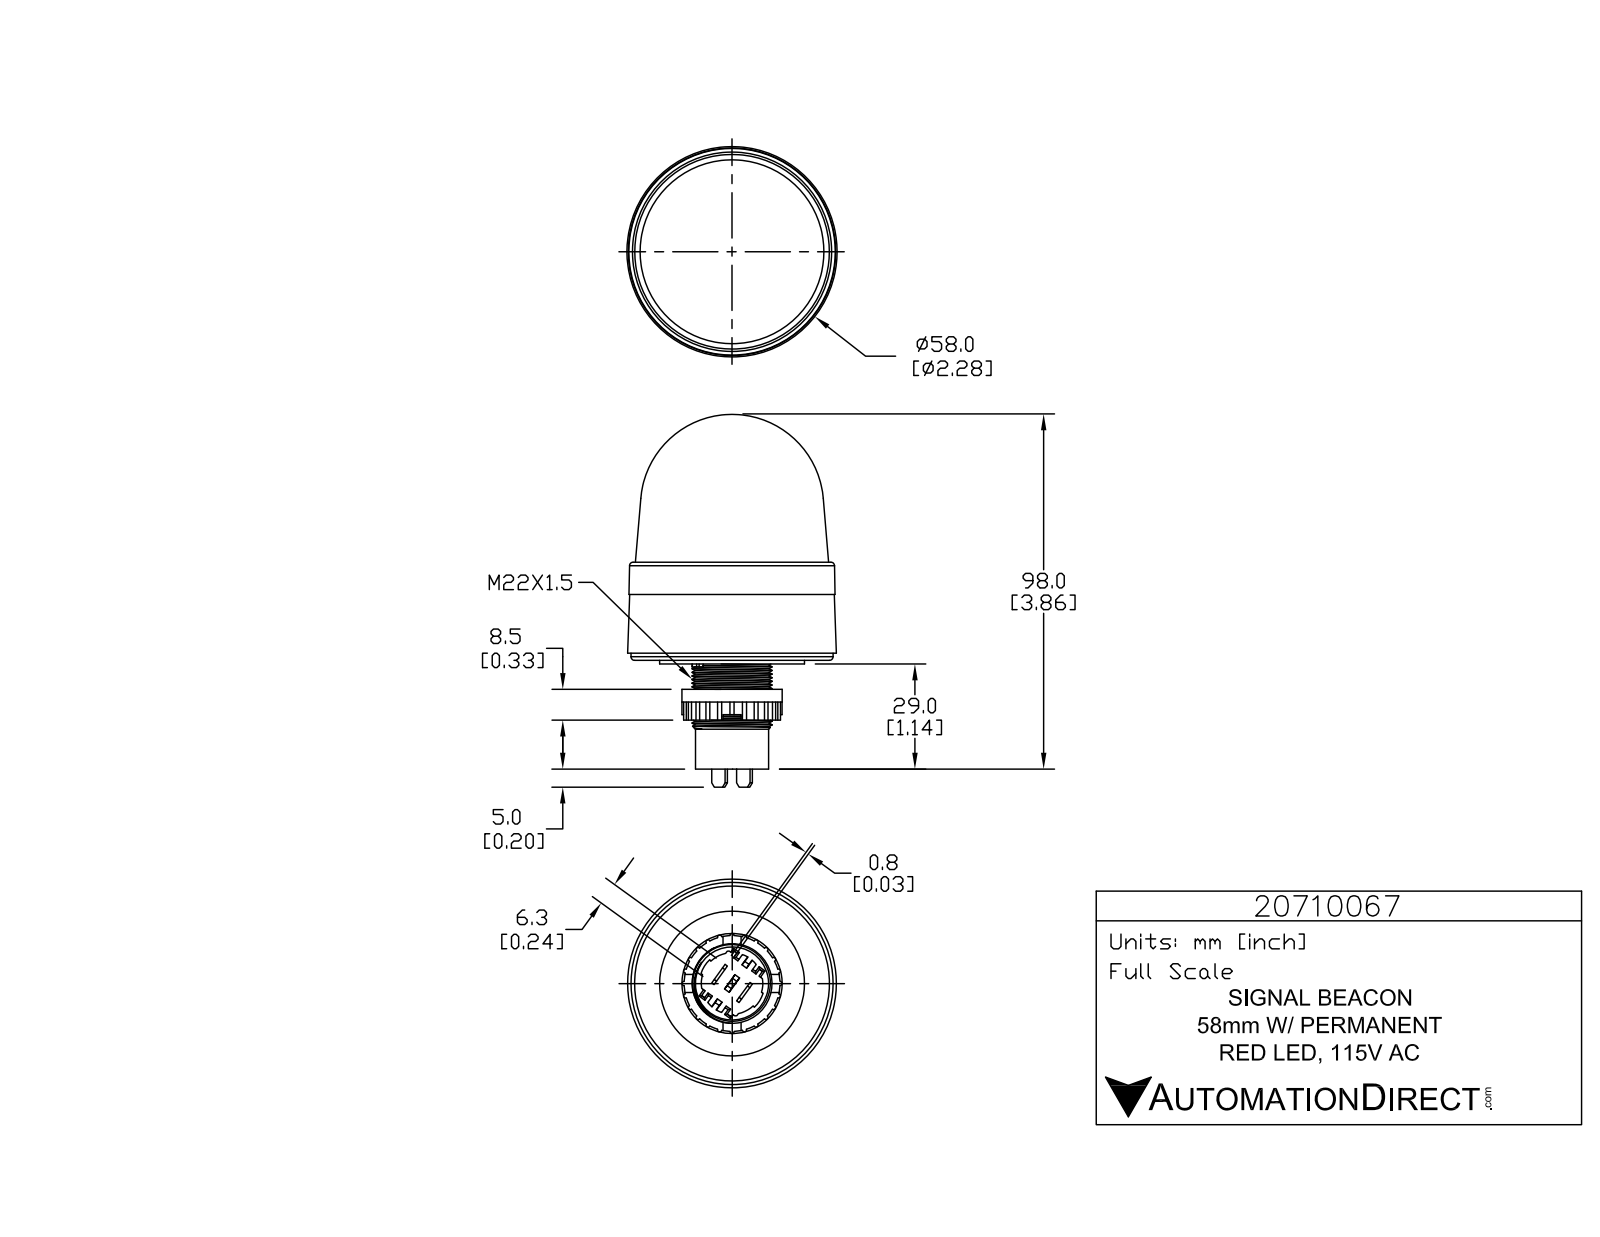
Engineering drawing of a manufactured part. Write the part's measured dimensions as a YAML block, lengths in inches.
part_name: "20710067"
step_written_by: "SolidWorks 2015 (AUTOMOTIVE_DESIGN)"
units: inches
bodies: {solids: 1, faces: 266, planar: 119, cylindrical: 120, other: 27}
overall_size: [4.051, 2.269, 2.269]
volume: 9.016
surface_area: 31.05
round_holes:
  - {diameter: 0.906, count: 1}
round_bosses_or_shafts:
  - {diameter: 2.197, count: 1}
  - {diameter: 1.575, count: 1}
  - {diameter: 1.091, count: 1}
  - {diameter: 0.866, count: 1}
  - {diameter: 0.795, count: 1}
partial_cylinders:
  - {radius: 0.023, count: 24}
  - {radius: 0.02, count: 2}
  - {radius: 0.335, count: 1}
  - {radius: 0.354, count: 1}
  - {radius: 0.522, count: 1}
face_to_face_distances: [0.039, 0.276, 0.118, 1.142, 0.335, 0.315, 1.063, 0.748, 1.024, 0.728]
